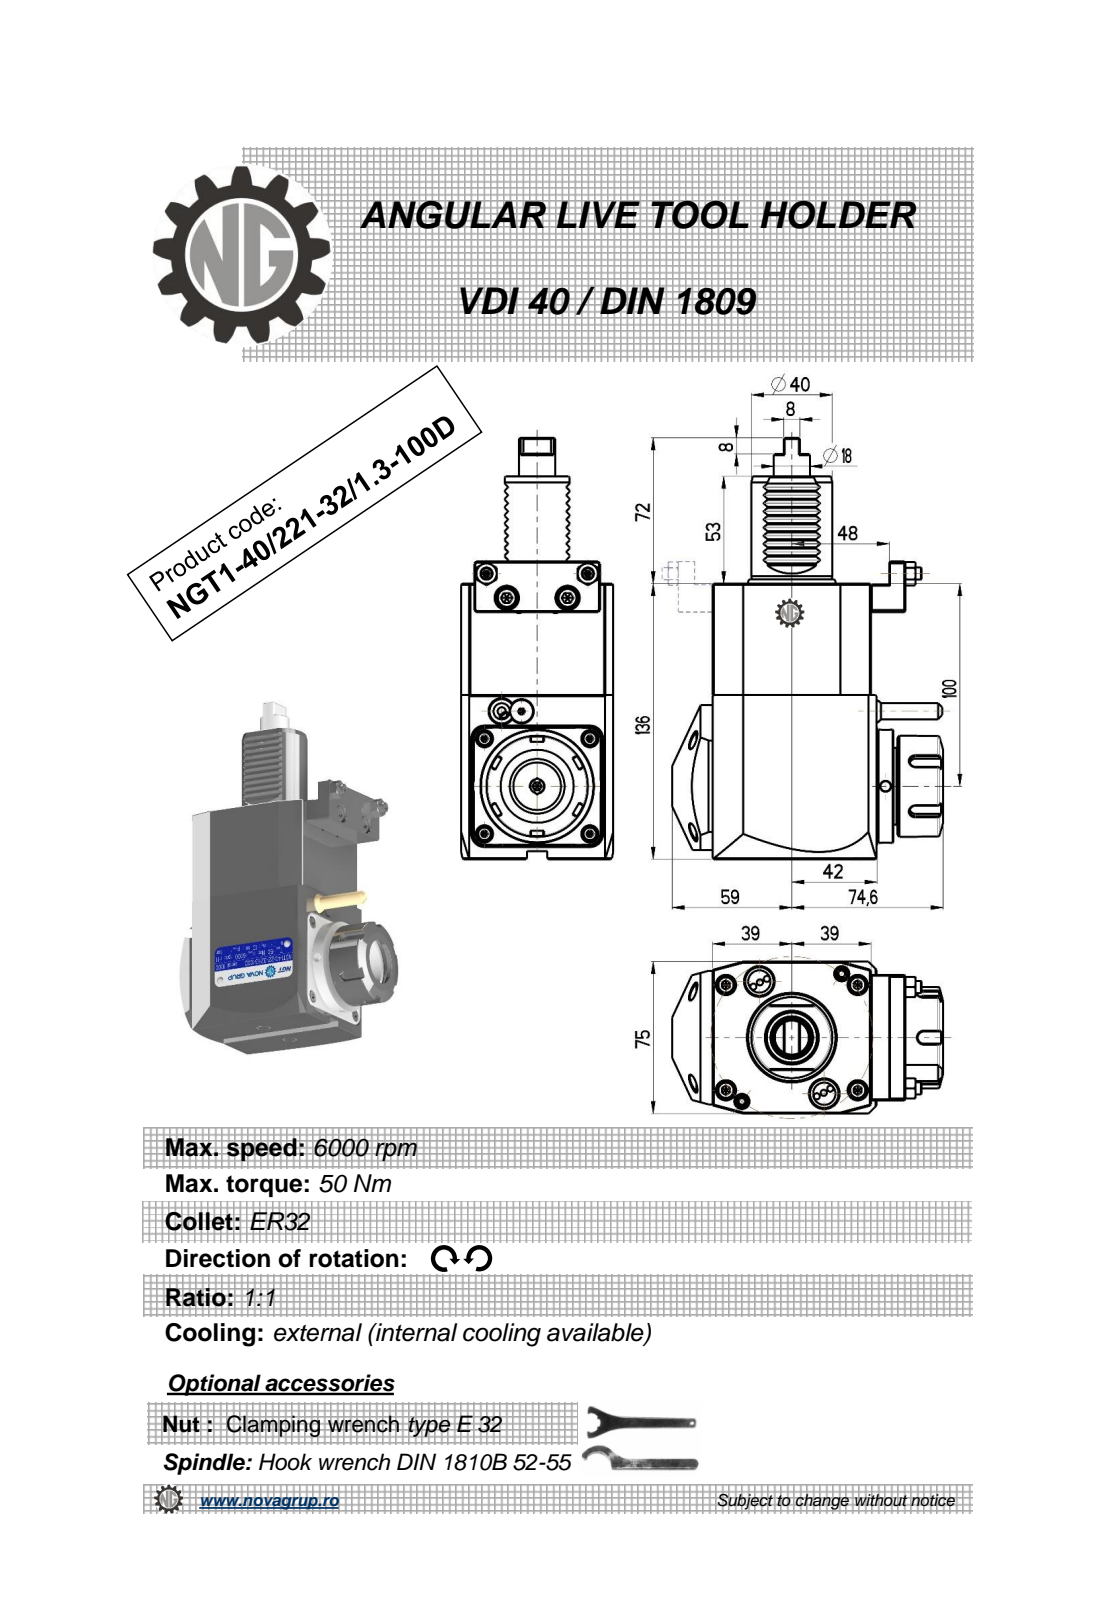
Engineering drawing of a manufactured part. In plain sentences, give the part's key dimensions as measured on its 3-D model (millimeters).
The part is named "NGT1_40_221_32_1_3_100D". Its 3-D file was written by "PRO/ENGINEER BY PARAMETRIC TECHNOLOGY CORPORATION, 2010280 (CONFIG_CONTROL_DESIGN)". It is 1 solid with 439 faces: 210 planar, 86 cylindrical and 143 other. Overall it measures 208 by 133.6 by 75 millimeters. Its volume is 996 592 cubic millimeters and its surface area 79 128 square millimeters. Round holes: 3 of diameter 5, 1 of diameter 3, 1 of diameter 27, 1 of diameter 42. Round bosses or shafts: 2 of diameter 6, 1 of diameter 56, 1 of diameter 50, 1 of diameter 41.4, 1 of diameter 41, 1 of diameter 40, 1 of diameter 17.8, 1 of diameter 11.2. Partial cylindrical surfaces (rounded edges, fillets, slot ends): 20 of radius 0.3, 10 of radius 0.31, 6 of radius 0.22, 5 of radius 3, 2 of radius 0.8, 1 of radius 40. The main face-to-face distances are 75, 136, 78, 14, 81, 3, 11, 0.5, 8, 6. The hole center spacings are 40.93.
